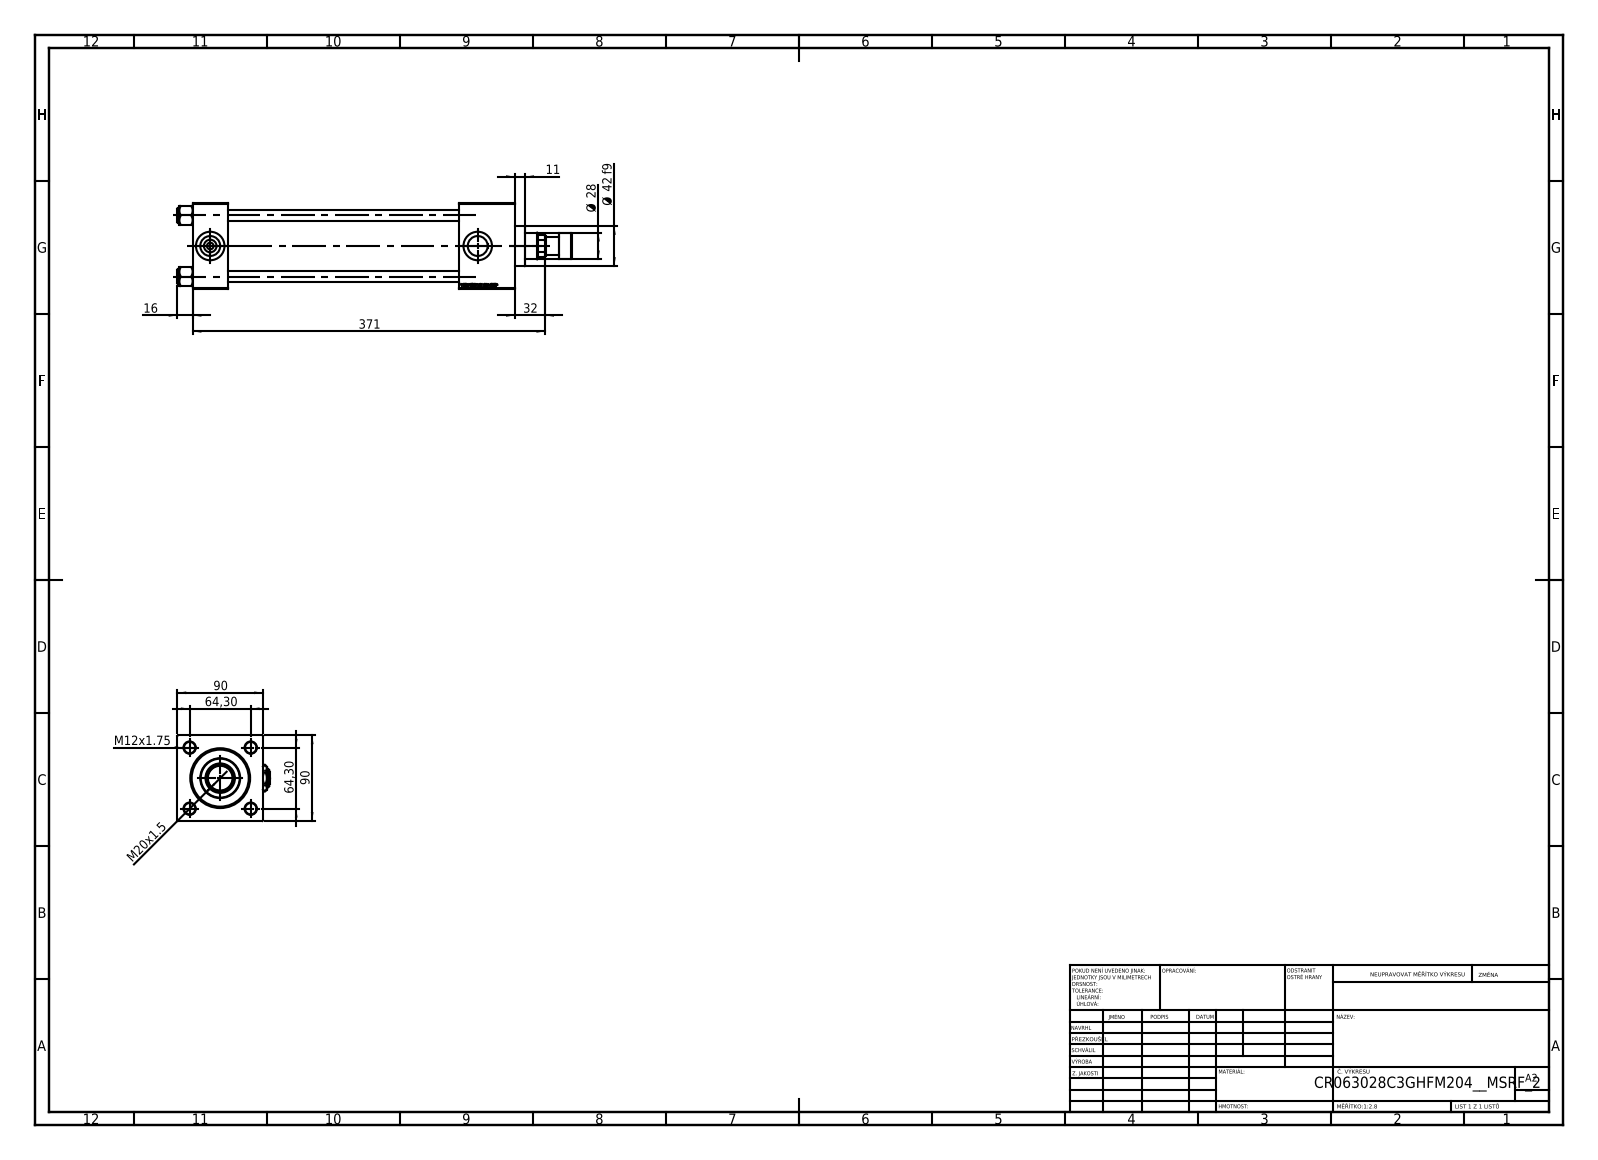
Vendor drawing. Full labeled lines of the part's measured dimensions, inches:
Part name (STEP PRODUCT): Zatka_pro_OIL_PORT; V215CR_C_Body; NUT_M5_C; V215CR_ROD_END_F (+3 more)
STEP written by: SolidWorks 2019 (CONFIG_CONTROL_DESIGN)
Units: inches
Bodies: 14 solids, 1264 faces (578 planar, 102 cylindrical, 584 other)
Overall size (bounding box): 16.339 × 3.819 × 3.543
Volume: 77.07 in³ · Surface area: 476.5 in²
Round holes (diameter × count): ⌀0.472 ×4, ⌀0.276 ×2, ⌀0.825 ×2, ⌀1.181 ×2, ⌀0.728 ×1, ⌀1.102 ×1, ⌀1.22 ×1, ⌀1.969 ×1, ⌀2.362 ×1, ⌀2.48 ×1
Round bosses / shafts (diameter × count): ⌀0.591 ×4, ⌀2.717 ×1, ⌀1.654 ×1, ⌀1.063 ×1, ⌀0.709 ×1
Main face-to-face distances: 3.543, 1.457, 11.89, 13.346, 2.323, 11.024, 9.567, 12.217, 10.76, 1.193
Hole centre spacings: 1.79, 2.531, 3.58, 11.083
